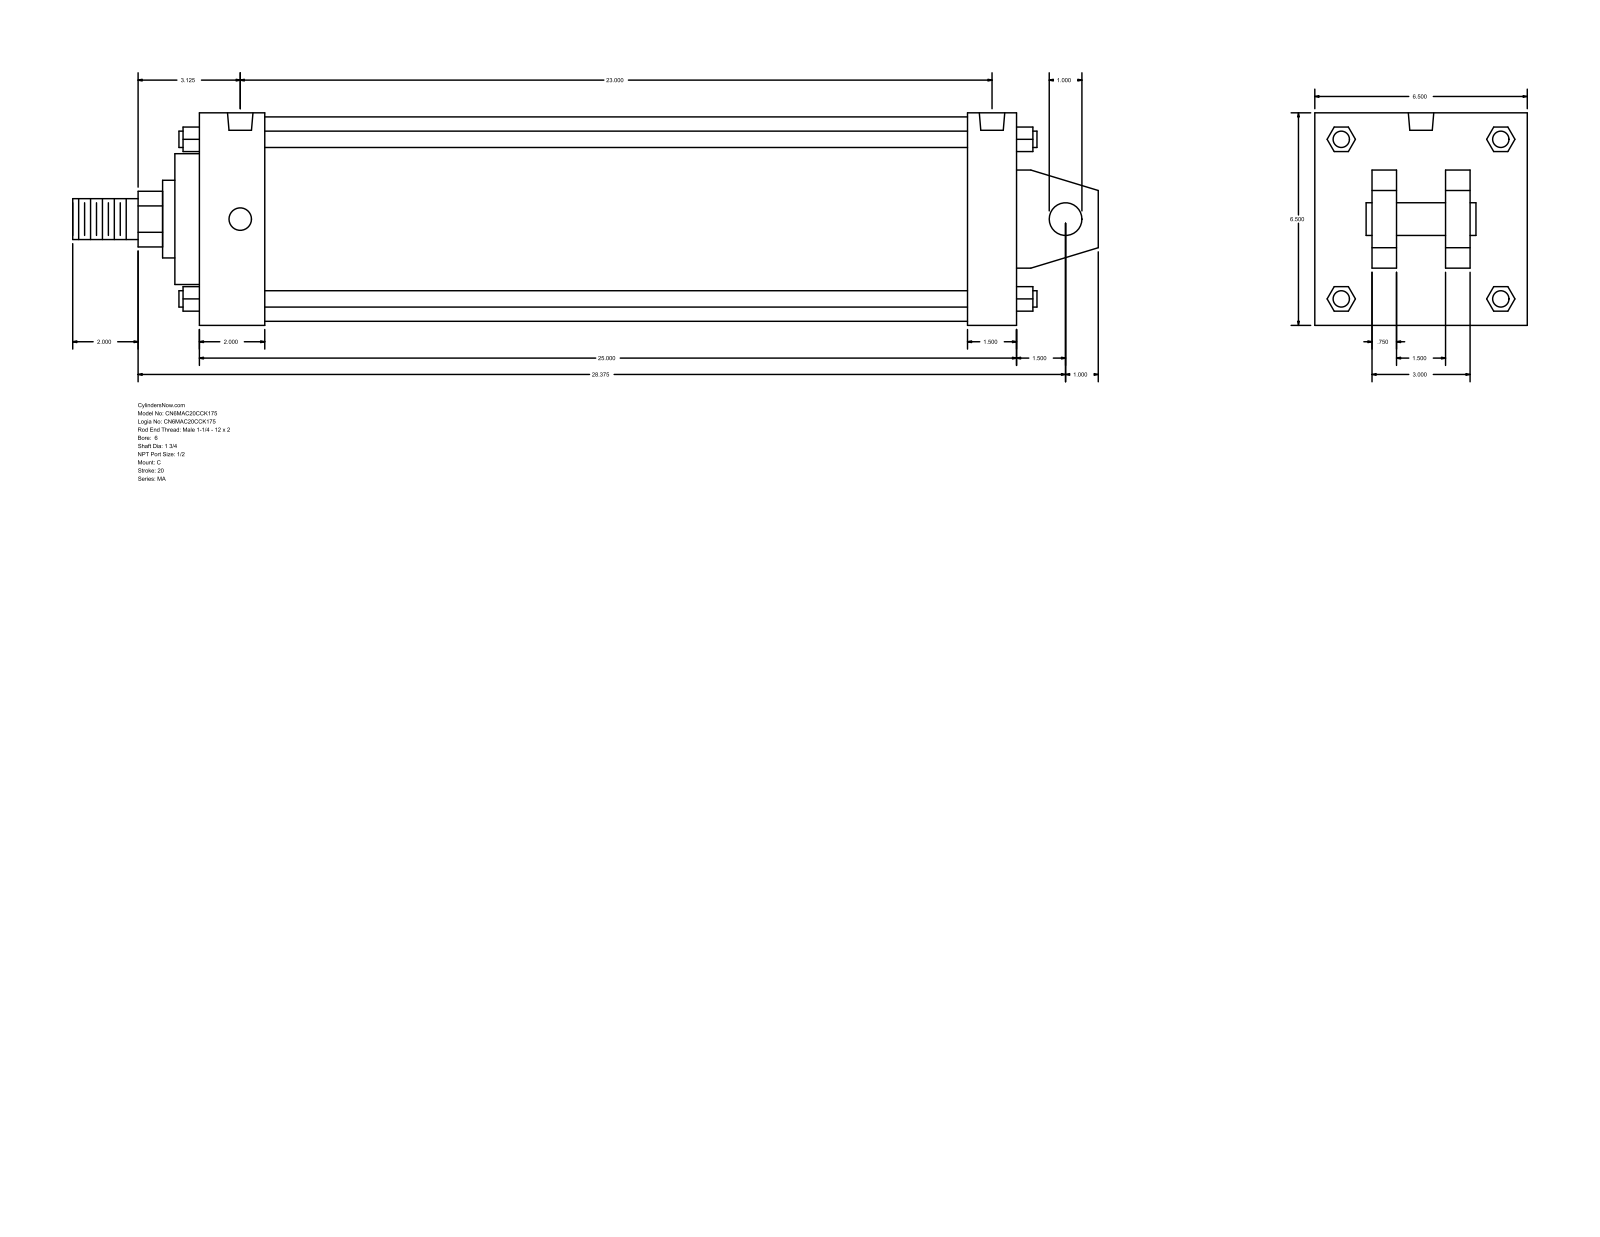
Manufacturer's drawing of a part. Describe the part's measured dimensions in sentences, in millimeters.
The part is named "MA_C__0600_1.75". Its 3-D file was written by "GSSL Pune (CONFIG_CONTROL_DESIGN)". It is 0 solids with 141 faces: 109 planar, 32 cylindrical and 0 other. Overall it measures 796.92 by 165.1 by 165.1 millimeters. Round holes: 4 of diameter 17.46, 2 of diameter 19.77. Round bosses or shafts: 4 of diameter 12.7, 1 of diameter 158.75, 1 of diameter 101.6, 1 of diameter 60.33, 1 of diameter 44.45, 1 of diameter 31.75, 1 of diameter 25.4. Partial cylindrical surfaces (rounded edges, fillets, slot ends): 1 of radius 21.63. The main face-to-face distances are 165.1, 635, 19.05, 38.1, 63.5, 101.6, 44.45, 120.65, 57.15, 50.8. The hole center spacings are 584.2.
